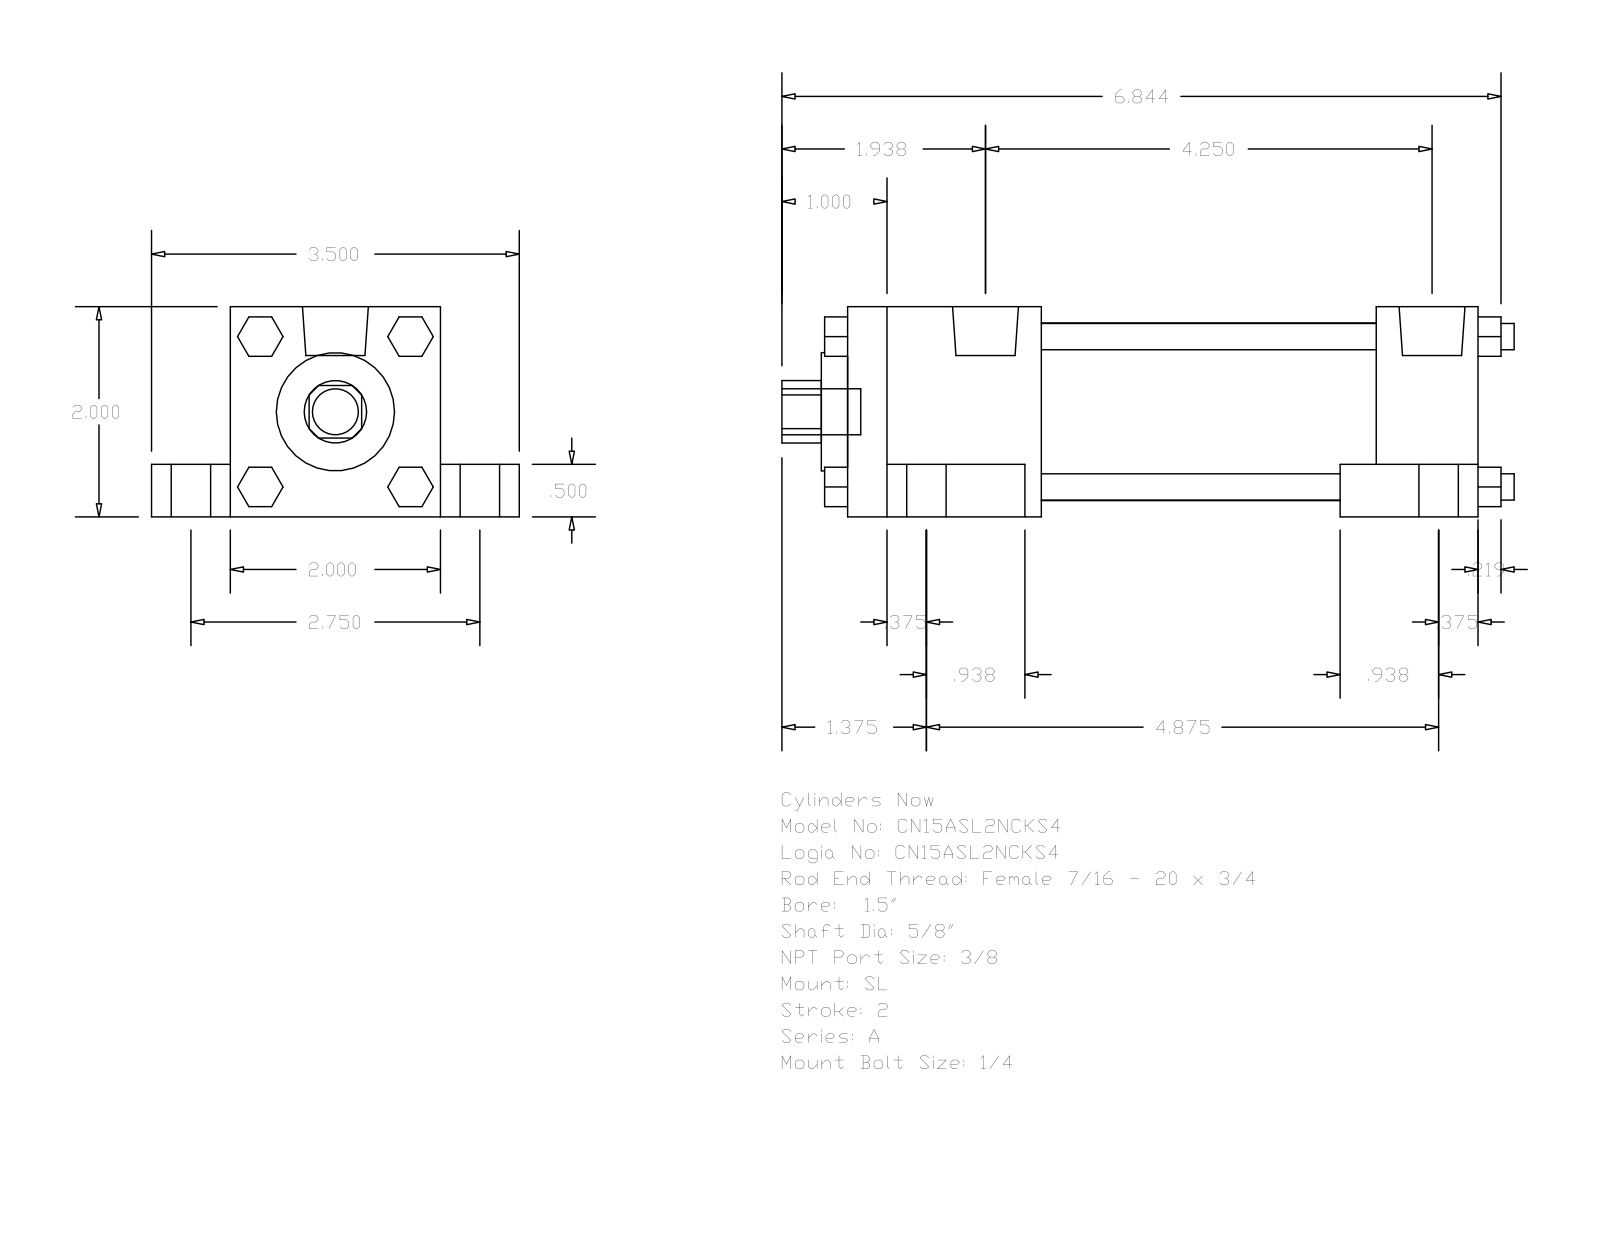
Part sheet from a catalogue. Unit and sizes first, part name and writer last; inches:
Units: inches
Overall size (bounding box): 6.969 × 3.5 × 2
Round holes (diameter × count): ⌀0.625 ×1, ⌀1.125 ×1, ⌀1.69 ×1
Round bosses / shafts (diameter × count): ⌀0.625 ×4, ⌀0.375 ×4, ⌀0.25 ×4, ⌀0.219 ×4, ⌀0.627 ×2, ⌀0.437 ×1
Partial cylindrical surfaces — rounded edges, fillets, slot ends (radius × count): R0.297 ×1
Main face-to-face distances: 2, 0.75, 0.5, 1.5, 2.75, 6, 0.375, 1.313, 5.031, 0.969
Bodies: 0 solids, 148 faces (112 planar, 36 cylindrical, 0 other)
Part name (STEP PRODUCT): A_SL__0150_0.625
STEP written by: GSSL Pune (CONFIG_CONTROL_DESIGN)
